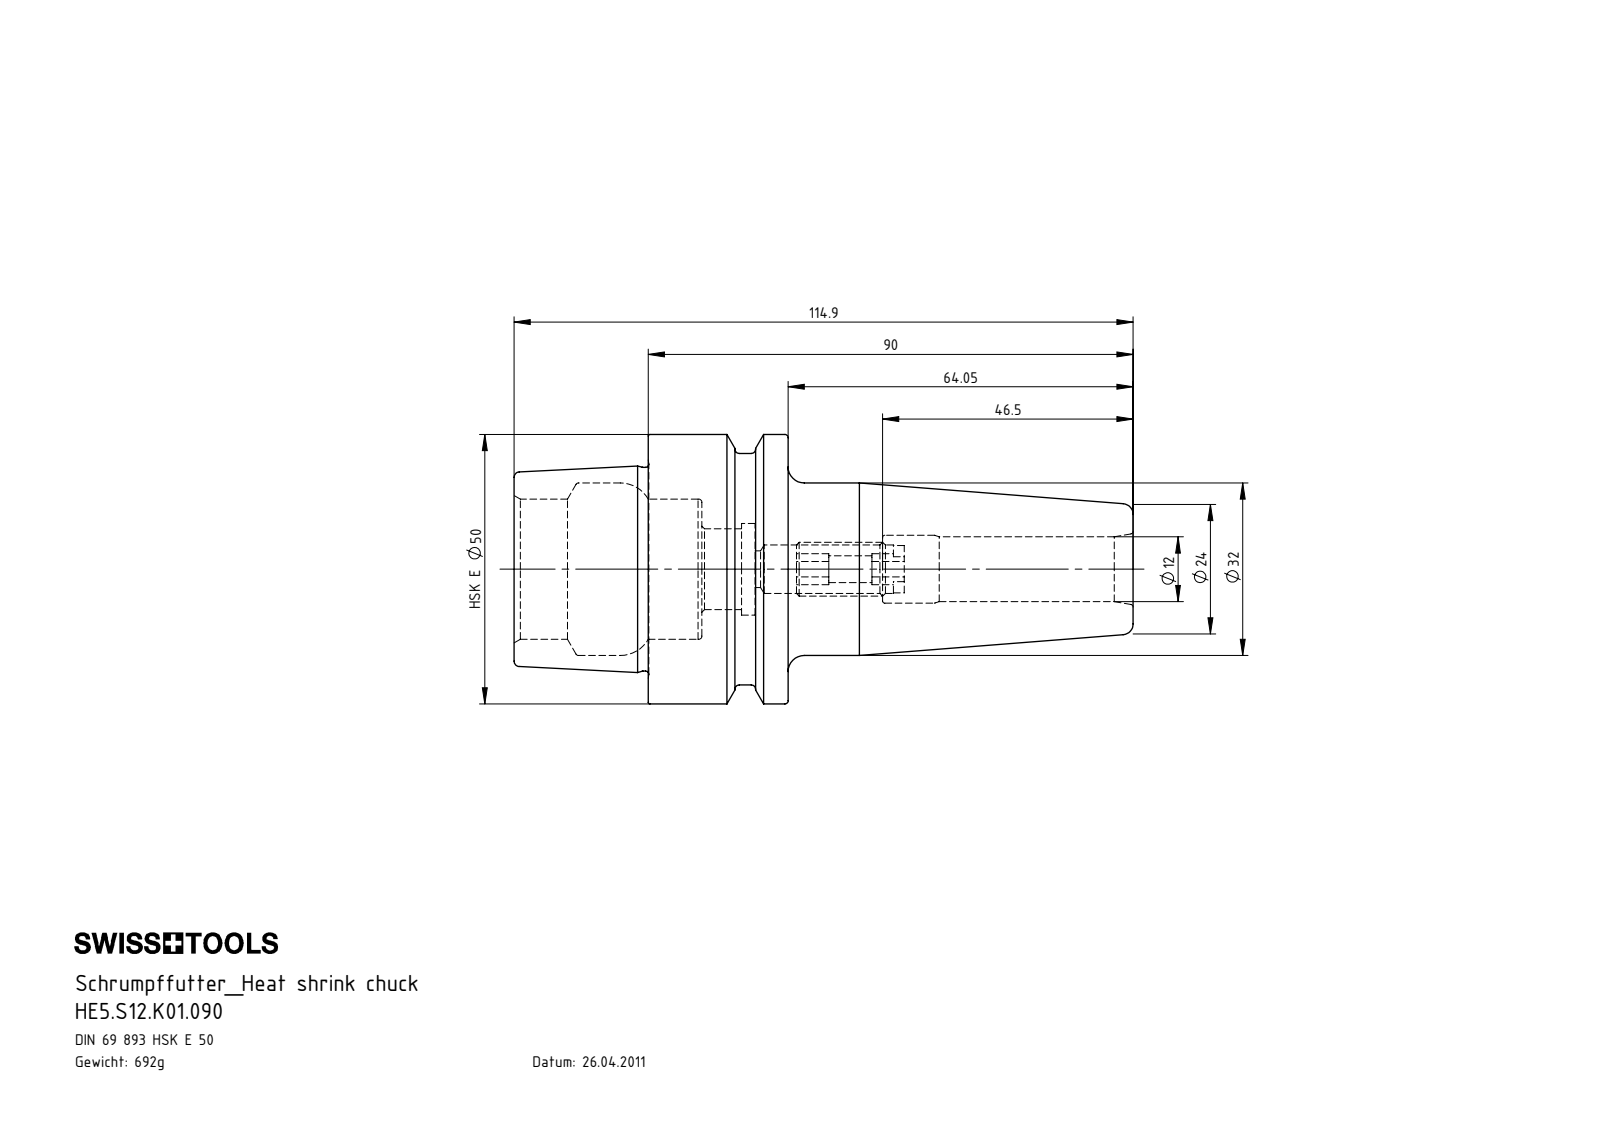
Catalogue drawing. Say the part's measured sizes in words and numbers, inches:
The part is named "HE5-S12.K01.090; ERU-AN4.K01.020_A; HE5-S12.K01.090_B_Fertigbearbeitung". Its 3-D file was written by "SolidWorks 2012 (AUTOMOTIVE_DESIGN)". It is 2 solids with 137 faces: 43 planar, 34 cylindrical and 60 other. Overall it measures 4.524 by 1.969 by 1.969 inches. Its volume is 5.381 cubic inches and its surface area 36.73 square inches. Round holes: 1 of diameter 0.197, 1 of diameter 0.268, 1 of diameter 0.354, 1 of diameter 0.472, 1 of diameter 0.496, 1 of diameter 0.591, 1 of diameter 0.669, 1 of diameter 1.024, 1 of diameter 1.26. Round bosses or shafts: 1 of diameter 1.969, 1 of diameter 1.691, 1 of diameter 1.489, 1 of diameter 0.394. The main face-to-face distances are 1.022, 0.98, 2.002, 0.63, 1.372, 0.392, 1.76, 0.78, 0.388, 0.242.
